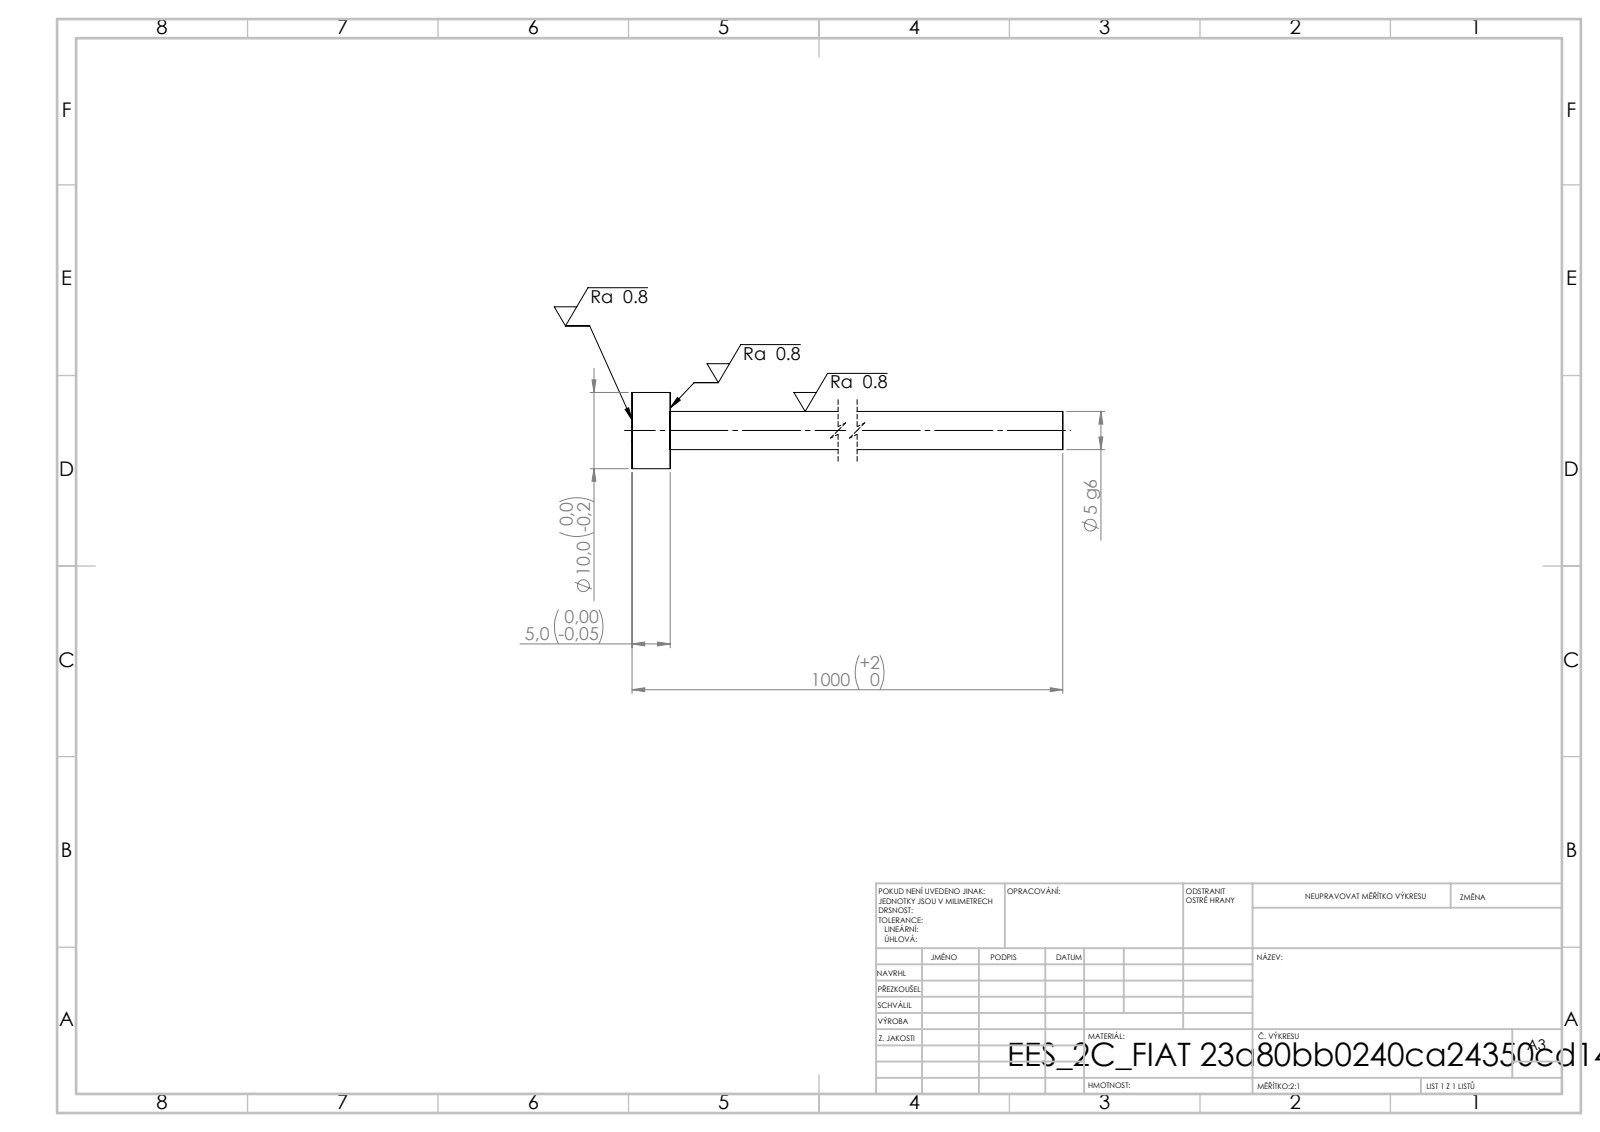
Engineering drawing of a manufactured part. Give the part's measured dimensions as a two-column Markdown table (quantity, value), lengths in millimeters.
| quantity | value |
| --- | --- |
| STEP written by | SolidWorks 2019 (CONFIG_CONTROL_DESIGN) |
| units | millimeters |
| bodies | 1 solid, 7 faces (3 planar, 4 cylindrical, 0 other) |
| overall size | 1000 × 10 × 10 |
| volume | 19 929 mm³ |
| surface area | 15 944 mm² |
| round bosses / shafts (diameter × count) | 10 × 1, 5 × 1 |
| main face-to-face distances | 5, 1000, 995 |
